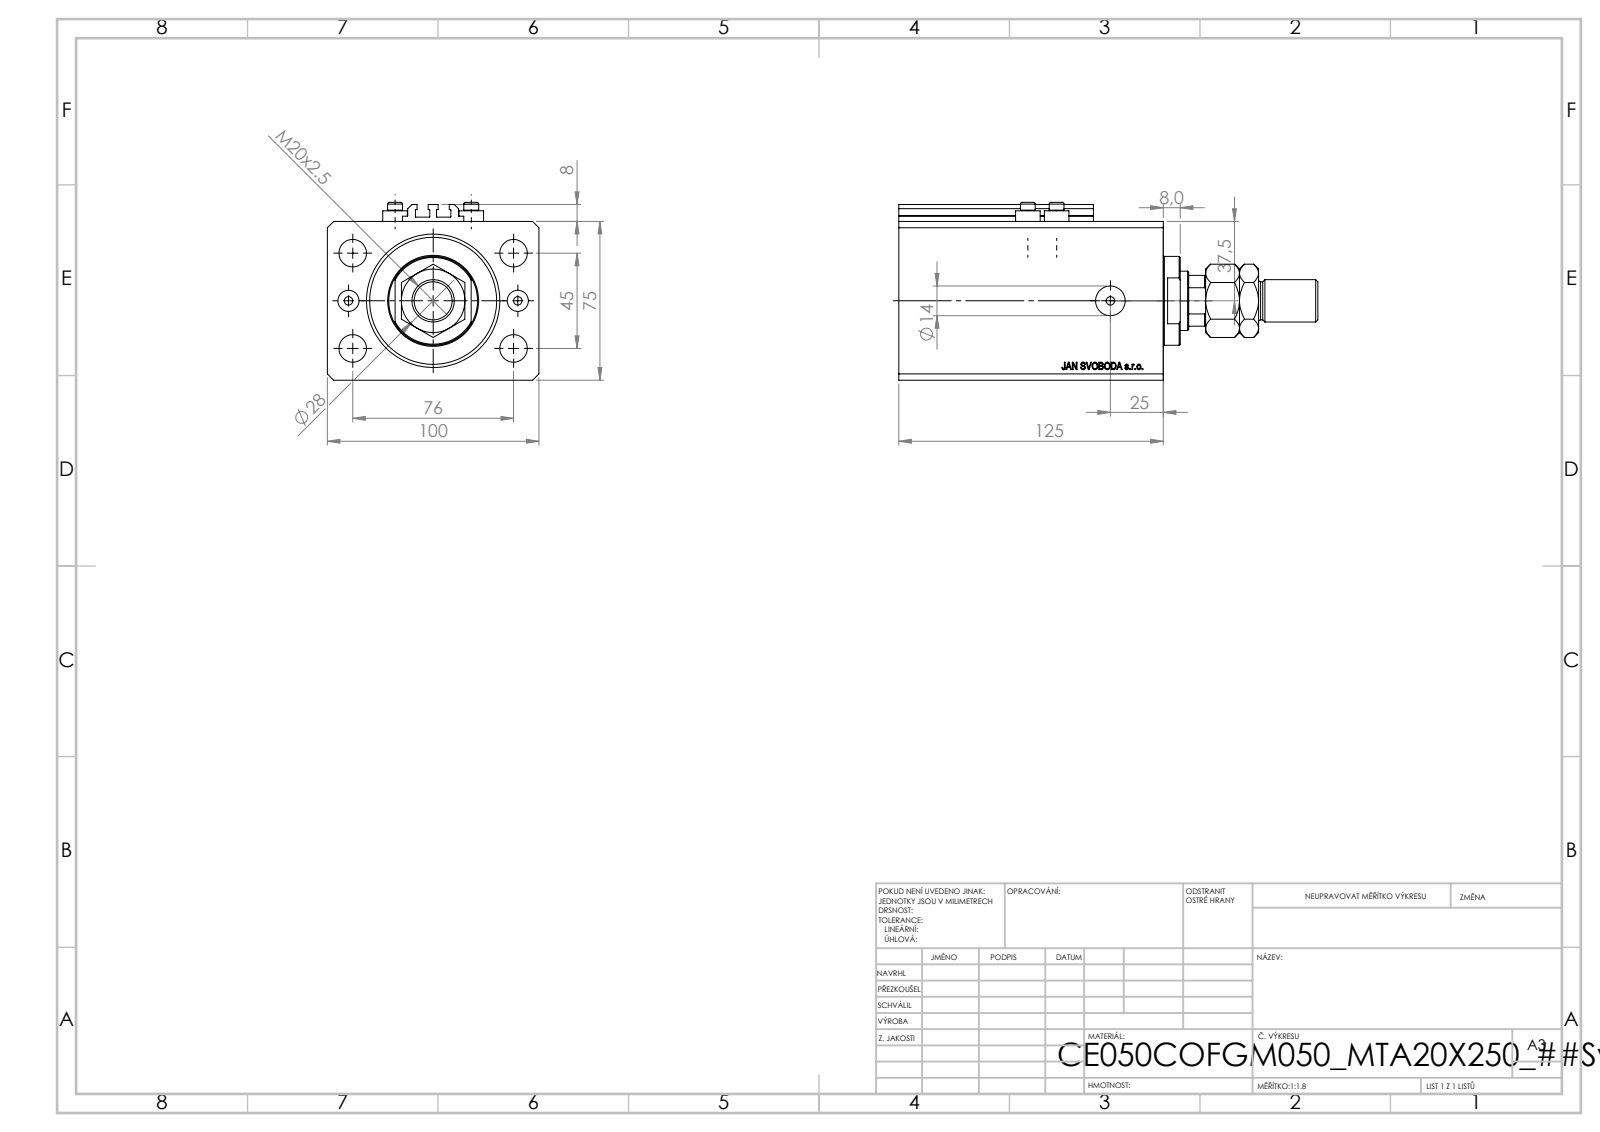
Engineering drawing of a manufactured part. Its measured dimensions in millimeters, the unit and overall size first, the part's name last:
Units: millimetres
Overall size (bounding box): 198 × 100 × 84
Round holes (diameter × count): ⌀4 ×8, ⌀13 ×4, ⌀10 ×2, ⌀14 ×2, ⌀18.5 ×1, ⌀28 ×1, ⌀50 ×1, ⌀63 ×1
Round bosses / shafts (diameter × count): ⌀11.6 ×4, ⌀7 ×4, ⌀42 ×1, ⌀20 ×1, ⌀18 ×1
Partial cylindrical surfaces — rounded edges, fillets, slot ends (radius × count): R0.2 ×10, R13.5 ×1
Main face-to-face distances: 75, 100, 125, 20, 11.9, 113.1, 105, 93.1, 3, 8
Hole centre spacings: 22.59, 44.16, 81.18, 13.6, 36, 38.48, 40, 45
Volume: 847 921 mm³ · Surface area: 148 401 mm²
Bodies: 9 solids, 1083 faces (519 planar, 90 cylindrical, 474 other)
Part name (STEP PRODUCT): MTA; V250CE_C_Body; V250CE_VC_C; V250CE_C_VCP (+1 more)
STEP written by: SolidWorks 2019 (CONFIG_CONTROL_DESIGN)
